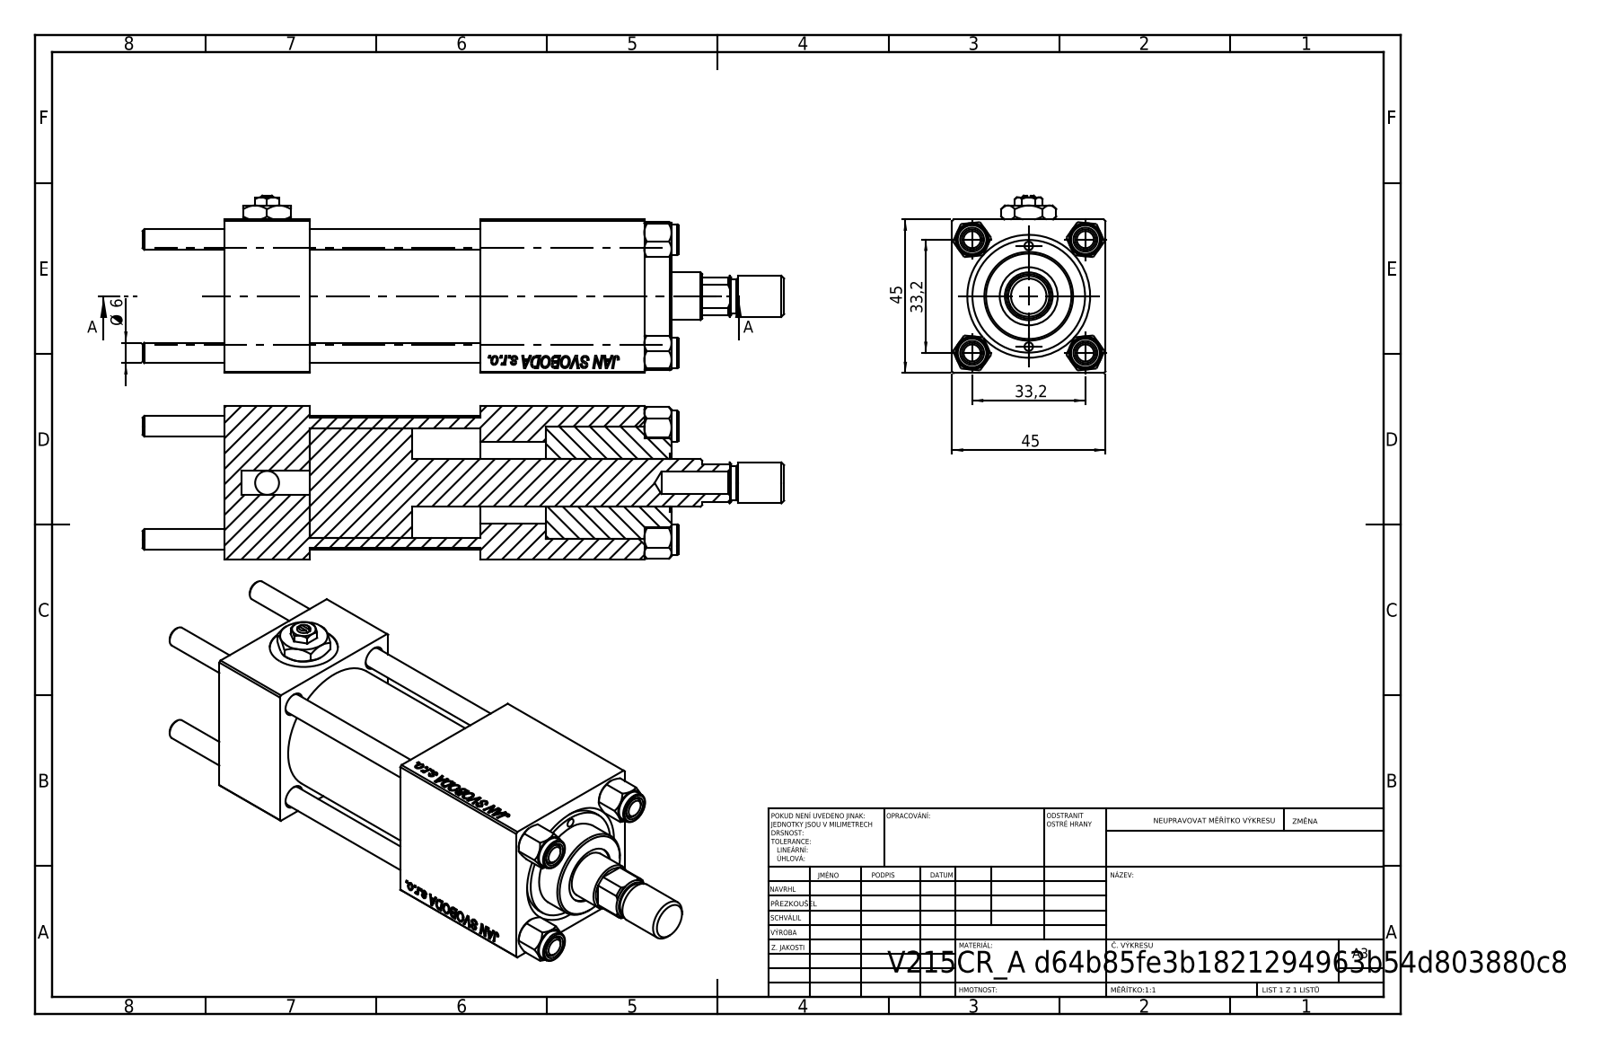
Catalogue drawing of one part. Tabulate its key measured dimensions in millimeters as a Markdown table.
| quantity | value |
| --- | --- |
| part name | NUT_M5; V215CR_VCP; CR025_012_A_0_G_A_G_M_020_+#_##_TYCINKA; Zatka_pro_OIL_PORT (+3 more) |
| STEP written by | SolidWorks 2019 (CONFIG_CONTROL_DESIGN) |
| units | millimeters |
| bodies | 13 solids, 1204 faces (548 planar, 92 cylindrical, 564 other) |
| overall size | 188 × 52 × 45 |
| volume | 199 139 mm³ |
| surface area | 74 831 mm² |
| round holes (diameter × count) | 6 × 4, 2.5 × 2, 7 × 2, 13.16 × 2, 20 × 2, 6.5 × 1, 14 × 1, 17 × 1, 24 × 1, 32 × 1, 33 × 1 |
| round bosses / shafts (diameter × count) | 9 × 4, 38 × 1, 26 × 1, 12 × 1, 10 × 1 |
| partial cylindrical surfaces (radius × count) | 6.5 × 1 |
| main face-to-face distances | 45, 25, 123, 98, 50, 75, 48, 94.3, 69.3, 19.3 |
| hole center spacings | 16.7, 23.48, 33.2, 35.47, 14.75, 46.95, 29.5, 75.5 |
